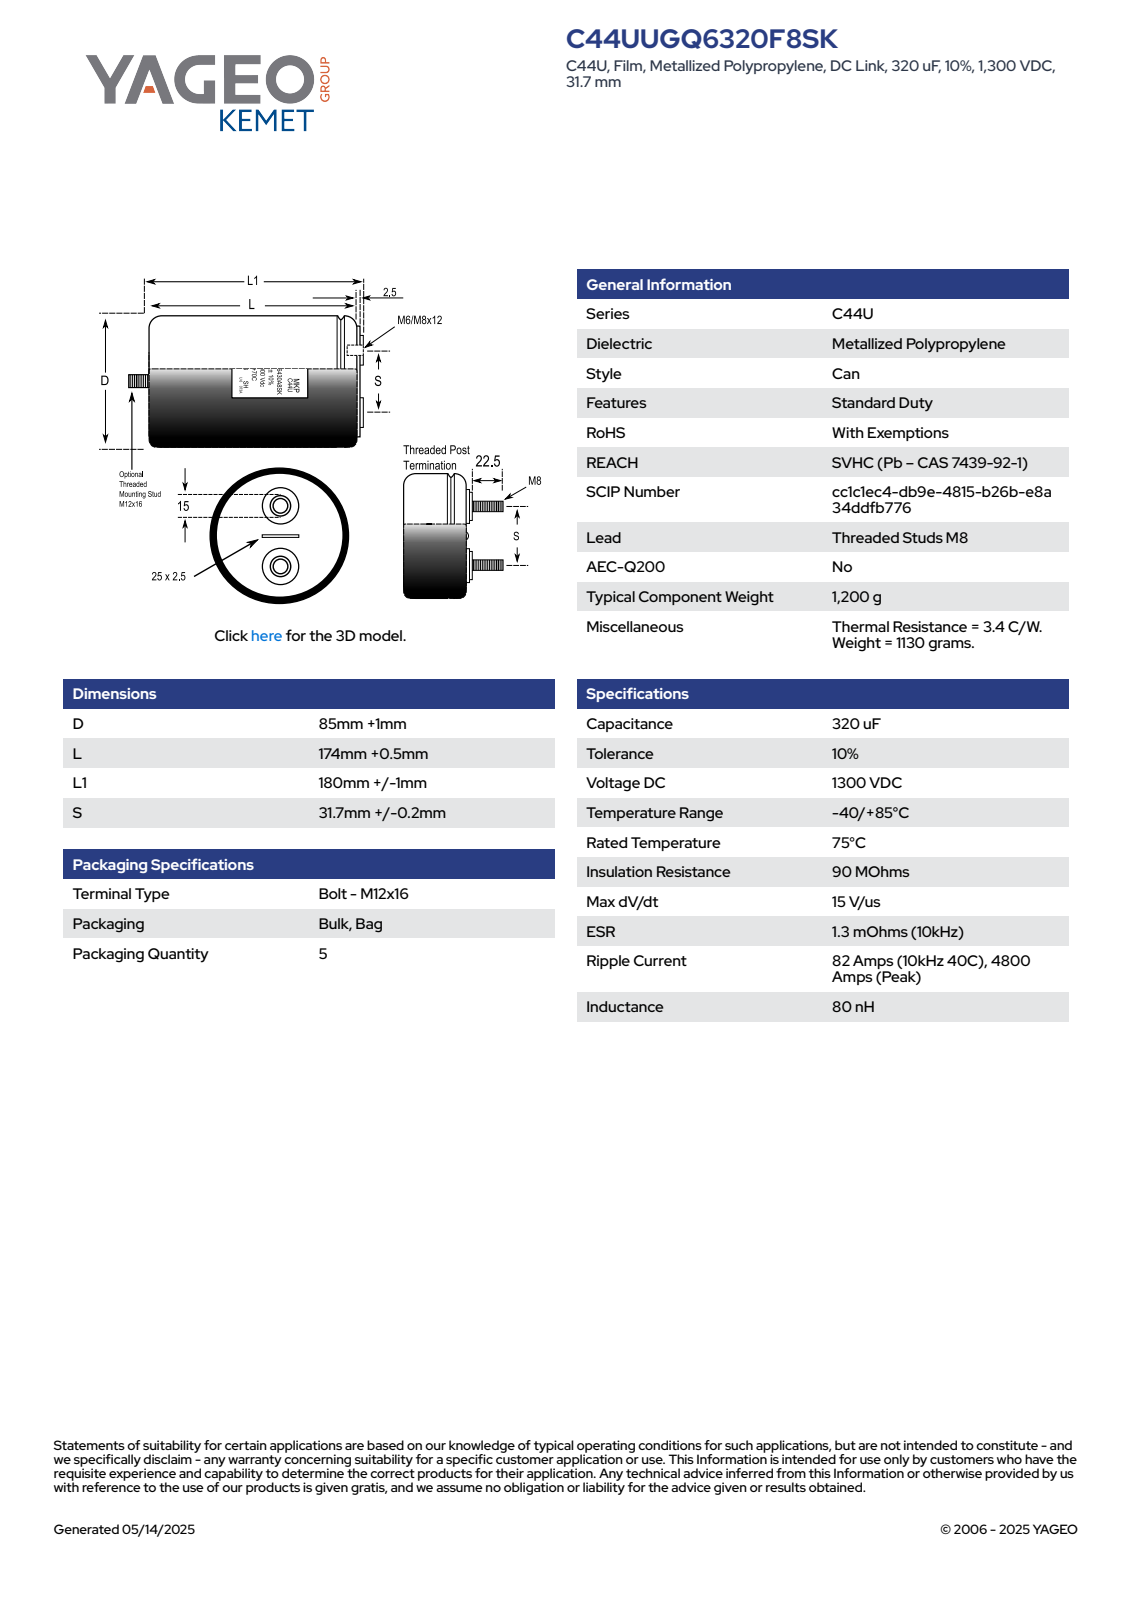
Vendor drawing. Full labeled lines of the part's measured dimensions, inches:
Part name (STEP PRODUCT): CFP_C44U_Q_85X174_D86L176S31.9
STEP written by: SolidWorks 2014 (AUTOMOTIVE_DESIGN)
Units: inches
Bodies: 1 solid, 104 faces (36 planar, 29 cylindrical, 39 other)
Overall size (bounding box): 8.543 × 3.386 × 3.386
Volume: 62.24 in³ · Surface area: 92.36 in²
Round bosses / shafts (diameter × count): ⌀0.709 ×2, ⌀0.591 ×2, ⌀0.315 ×2, ⌀3.386 ×1, ⌀2.756 ×1, ⌀0.472 ×1
Partial cylindrical surfaces — rounded edges, fillets, slot ends (radius × count): R1.693 ×1
Main face-to-face distances: 6.929, 0.049, 0.098, 7.028, 6.978, 0.63, 7.559, 7.608, 7.657, 0.984
